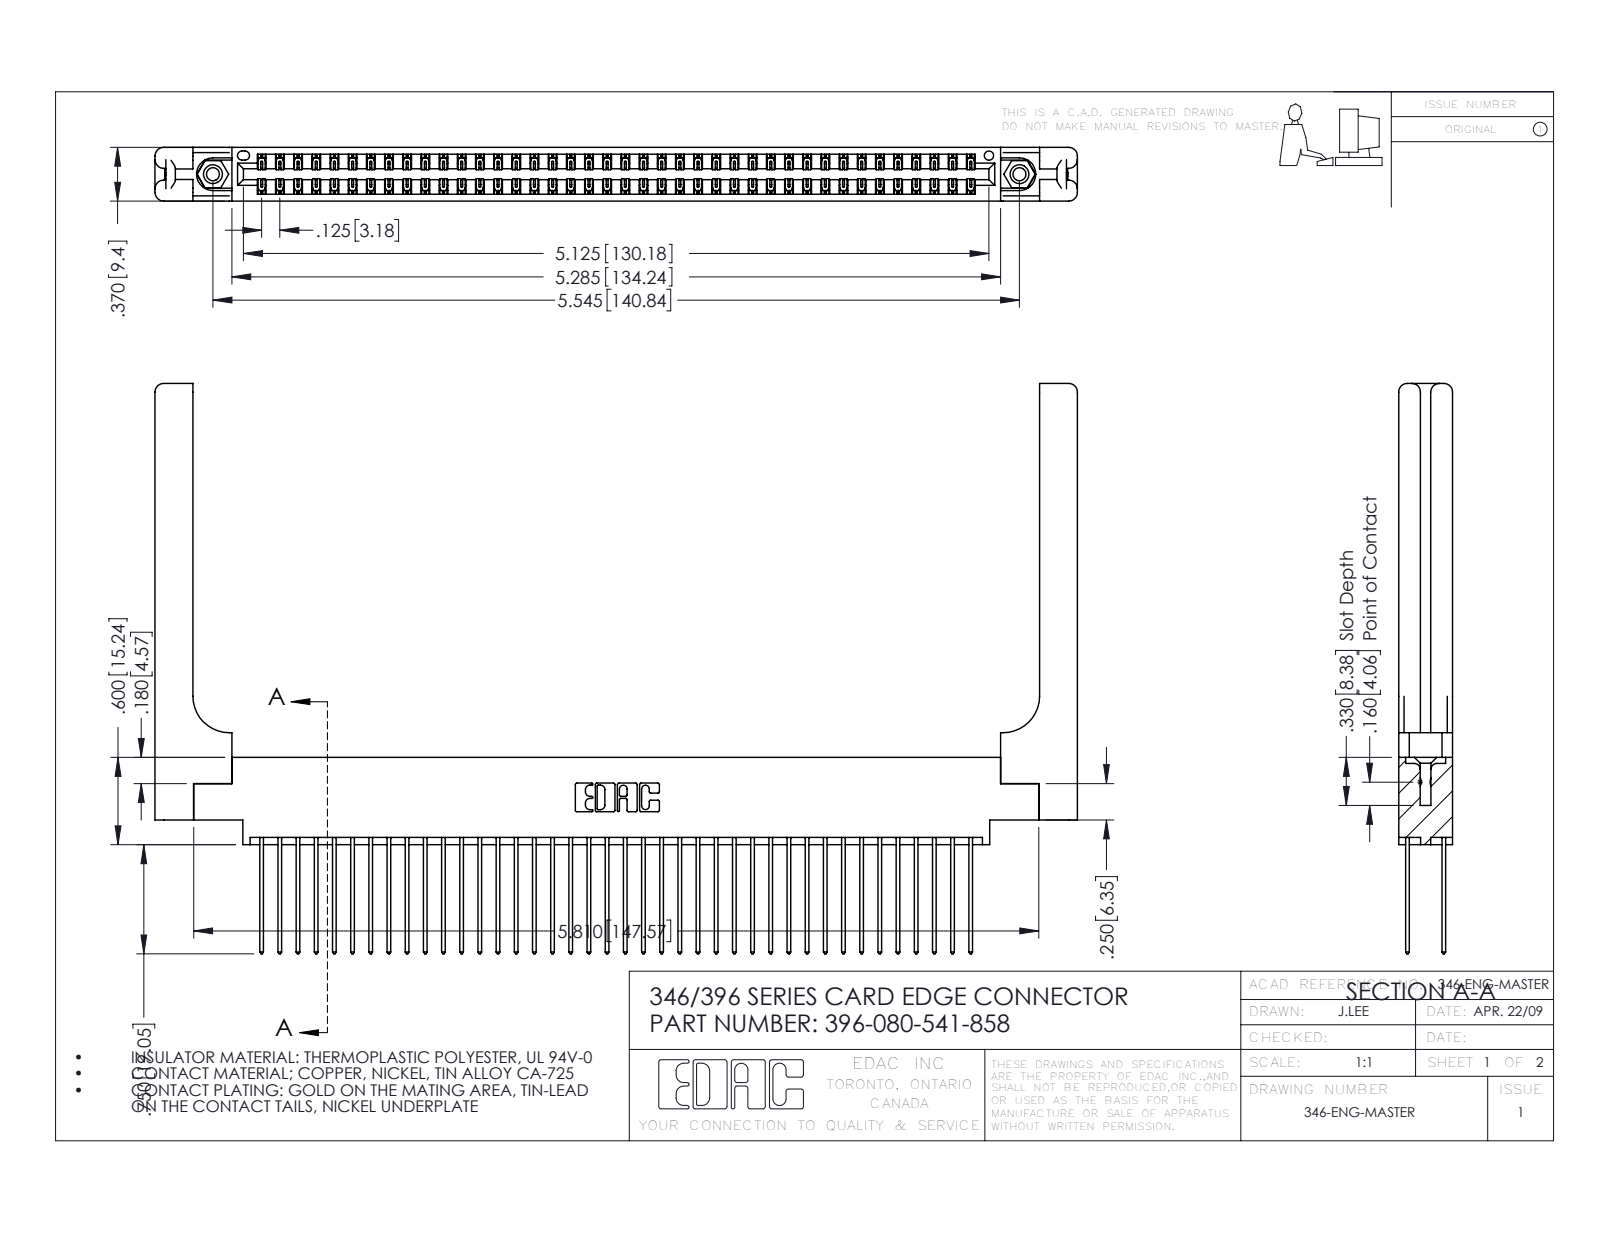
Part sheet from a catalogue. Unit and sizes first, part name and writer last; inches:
Units: inches
Overall size (bounding box): 6.341 × 3.92 × 0.37
Round holes (diameter × count): ⌀0.089 ×2, ⌀0.125 ×2, ⌀0.156 ×2, ⌀0.064 ×1
Round bosses / shafts (diameter × count): ⌀0.155 ×2
Partial cylindrical surfaces — rounded edges, fillets, slot ends (radius × count): R0.006 ×120, R0.01 ×80, R0.01 ×22, R0.06 ×16, R0.007 ×6, R0.031 ×6, R0.026 ×3, R0.014 ×2
Main face-to-face distances: 0.048, 0.322, 0.072, 0.37, 0.25, 0.025, 0.298, 0.15, 0.148, 0.275
Hole centre spacings: 0.246, 5.336, 5.545
Volume: 1.433 in³ · Surface area: 45.43 in²
Bodies: 85 solids, 4542 faces (3028 planar, 1454 cylindrical, 60 other)
Part name (STEP PRODUCT): 346 Part_0.170 Offset - 0.156 Dia-TH; 396-080-541-858; 345-292-001_345-293-141; 345-250-001_345-250-001-102 (+1 more)
STEP written by: SolidWorks 2016 (CONFIG_CONTROL_DESIGN)
